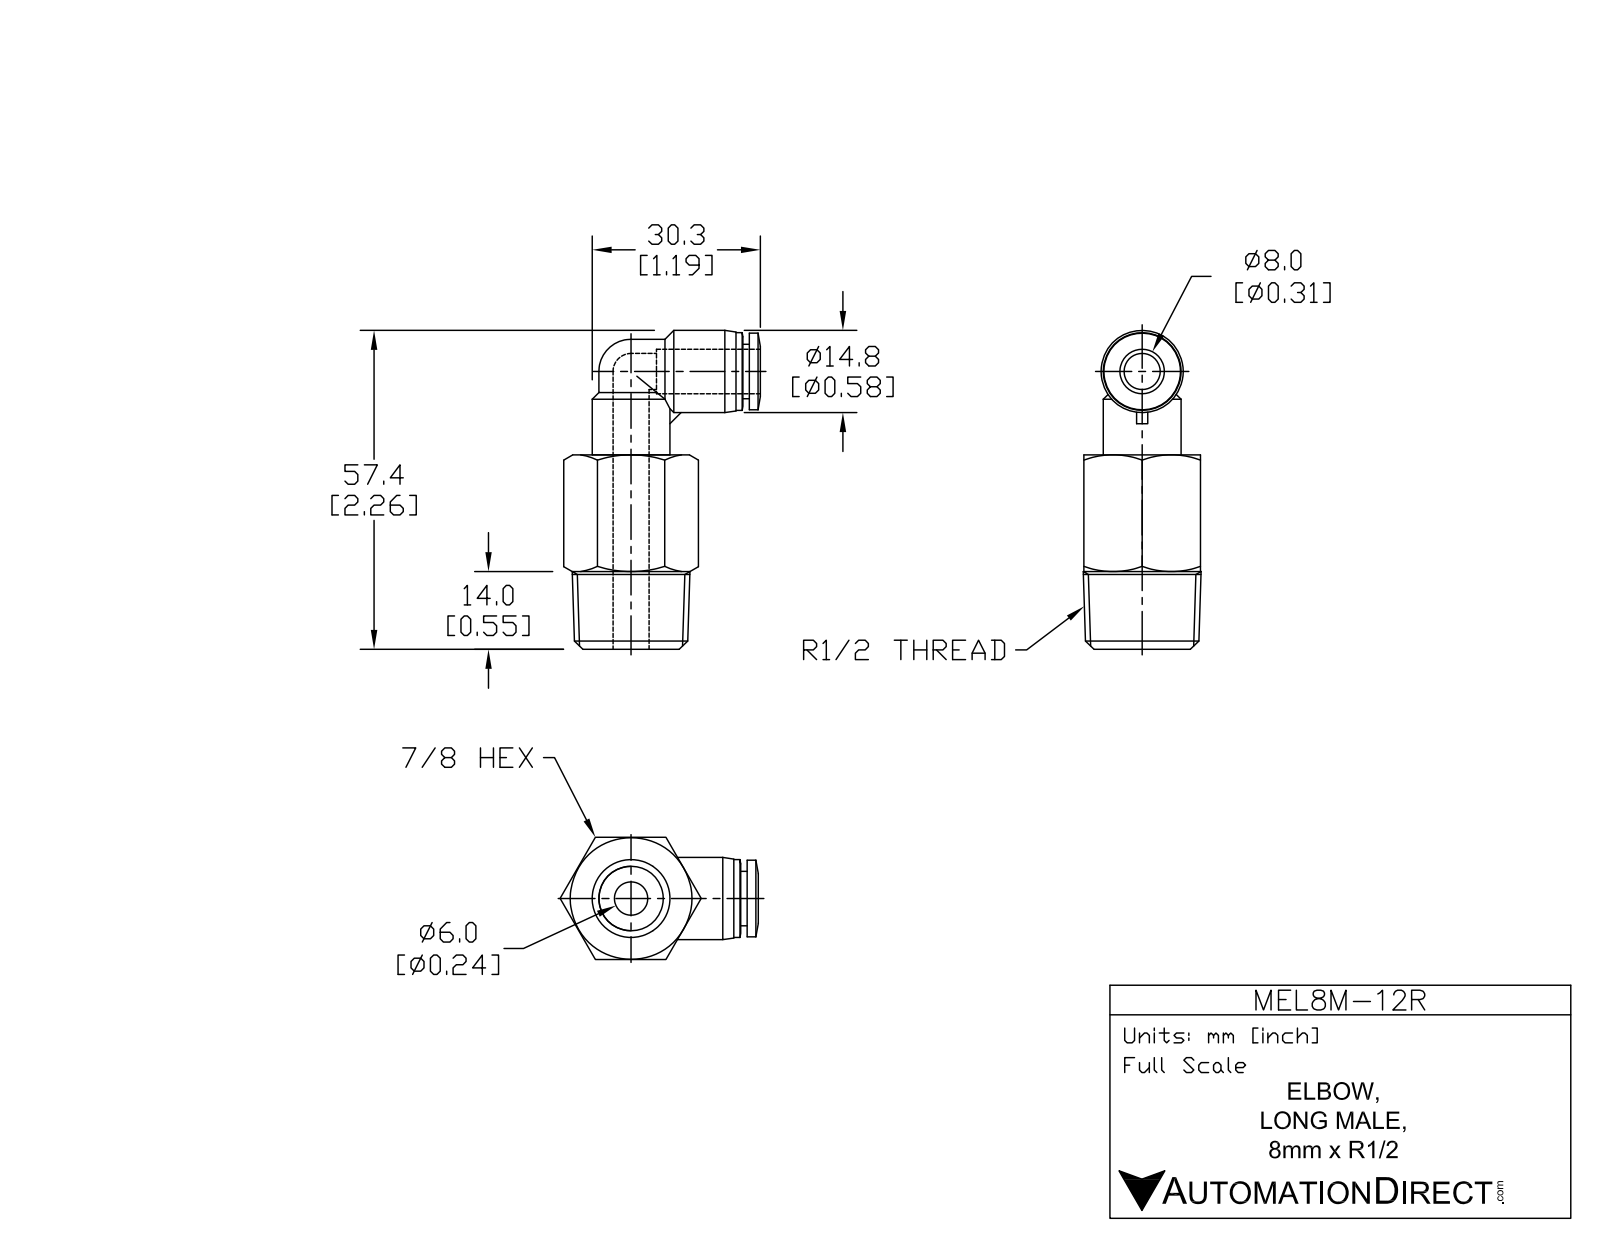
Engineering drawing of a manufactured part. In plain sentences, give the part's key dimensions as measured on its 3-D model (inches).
The part is named "MEL8M-12R". Its 3-D file was written by "SolidWorks 2015 (AUTOMOTIVE_DESIGN)". It is 1 solid with 69 faces: 17 planar, 19 cylindrical and 33 other. Overall it measures 2.26 by 1.402 by 0.866 inches. Its volume is 0.99 cubic inches and its surface area 9.904 square inches. Round holes: 2 of diameter 0.236, 1 of diameter 0.327. Round bosses or shafts: 2 of diameter 0.551, 1 of diameter 0.583, 1 of diameter 0.543, 1 of diameter 0.457, 1 of diameter 0.386. Partial cylindrical surfaces (rounded edges, fillets, slot ends): 1 of radius 0.228. The main face-to-face distances are 0.866, 1.378, 0.045, 0.551, 0.827, 0.596, 0.642, 0.079, 0.72, 0.124.
